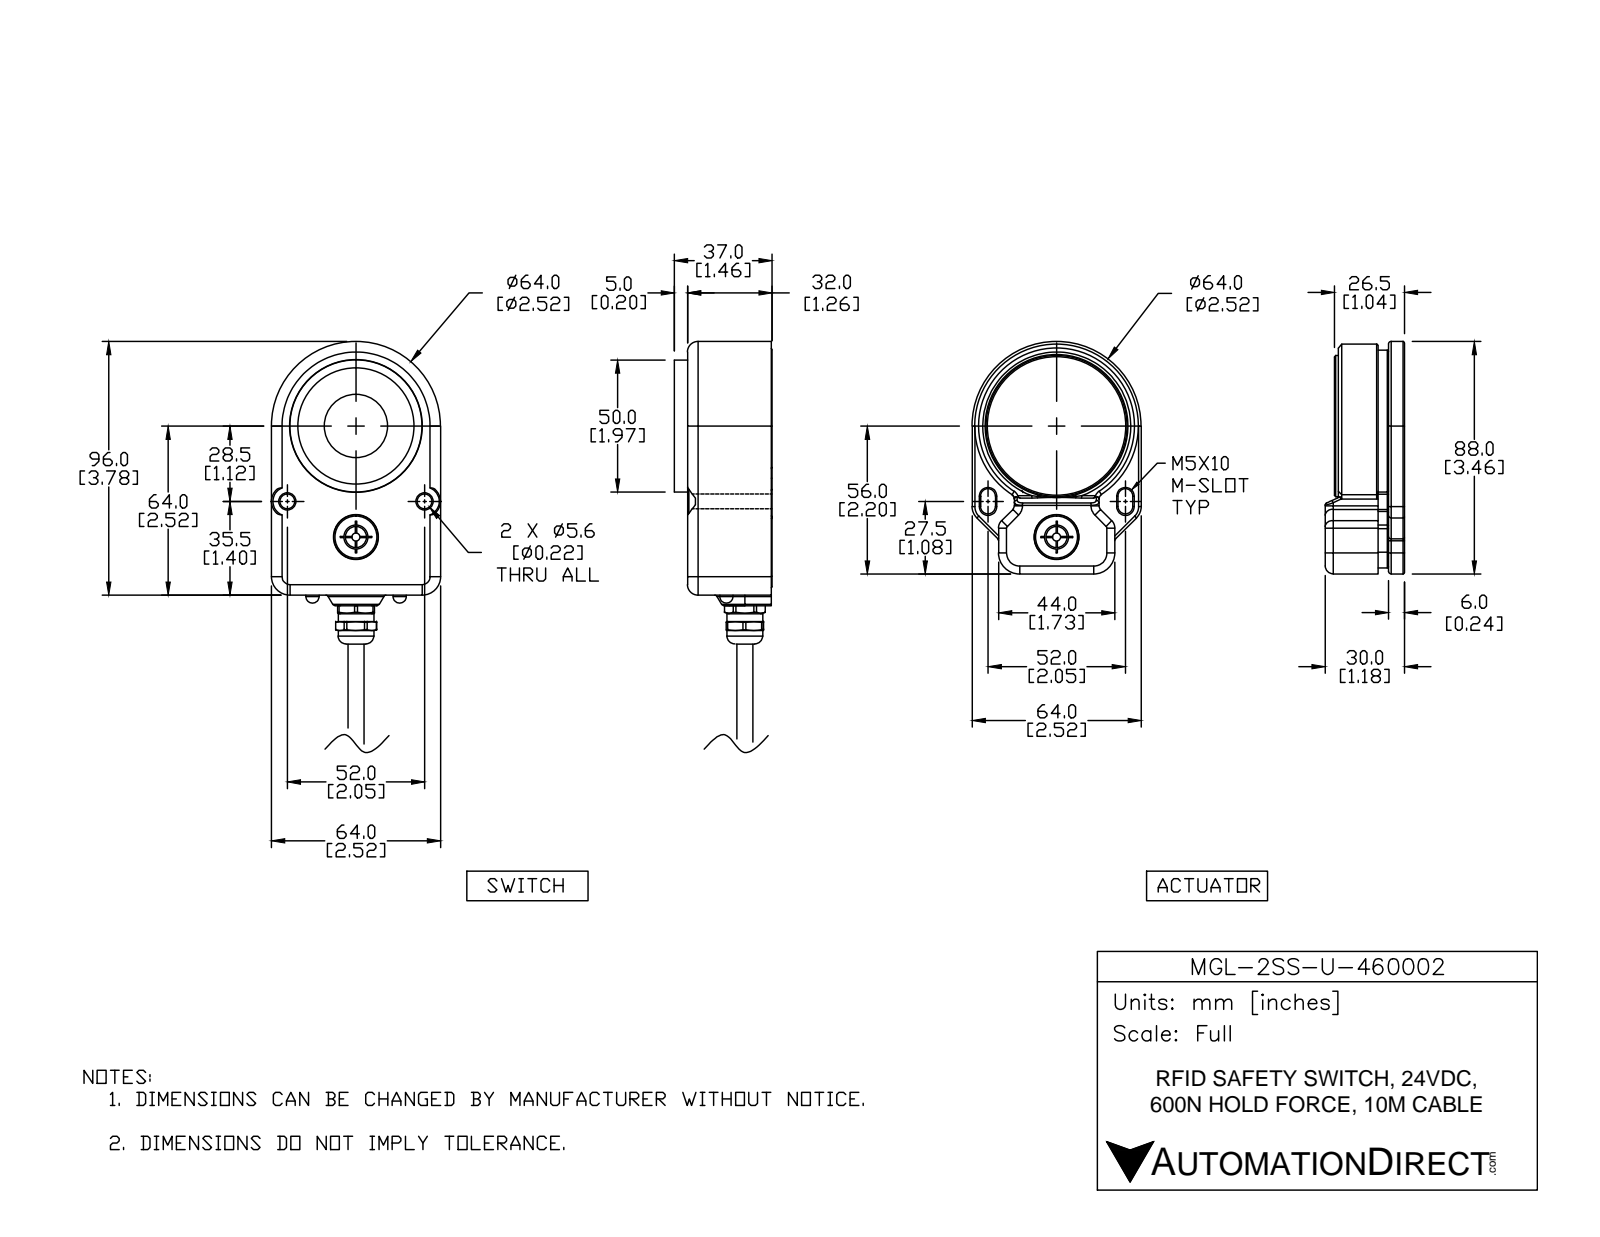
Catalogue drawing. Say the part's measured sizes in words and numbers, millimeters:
The part is named "MGL-2SS-U-460002; MGL-2SS-U-460002_1; MGL-2SS-U-460002_2". Its 3-D file was written by "SolidWorks 2017 (AUTOMOTIVE_DESIGN)". It is 20 solids with 1740 faces: 445 planar, 724 cylindrical and 571 other. Overall it measures 196 by 64.5 by 64 millimeters. Its volume is 205 300 cubic millimeters and its surface area 109 600 square millimeters. Round holes: 8 of diameter 2.5, 8 of diameter 4, 6 of diameter 3.3, 6 of diameter 8, 5 of diameter 5, 3 of diameter 9, 2 of diameter 5.6, 2 of diameter 10.5, 2 of diameter 17, 1 of diameter 6.4, 1 of diameter 6.7, 1 of diameter 6.8. Round bosses or shafts: 4 of diameter 0.5, 2 of diameter 6, 2 of diameter 5.8, 2 of diameter 5.6, 2 of diameter 3, 1 of diameter 62, 1 of diameter 57.4, 1 of diameter 53.4. Partial cylindrical surfaces (rounded edges, fillets, slot ends): 218 of radius 0.5, 69 of radius 1, 30 of radius 2, 17 of radius 0.3, 15 of radius 3, 12 of radius 4, 8 of radius 6, 7 of radius 0.6. The main face-to-face distances are 2.5, 6, 10.5, 3, 48, 19, 26.5, 10, 29, 2. The hole center spacings are 17.9, 19.5, 27.6, 26, 54.5, 8.8, 9.6, 9.7.
